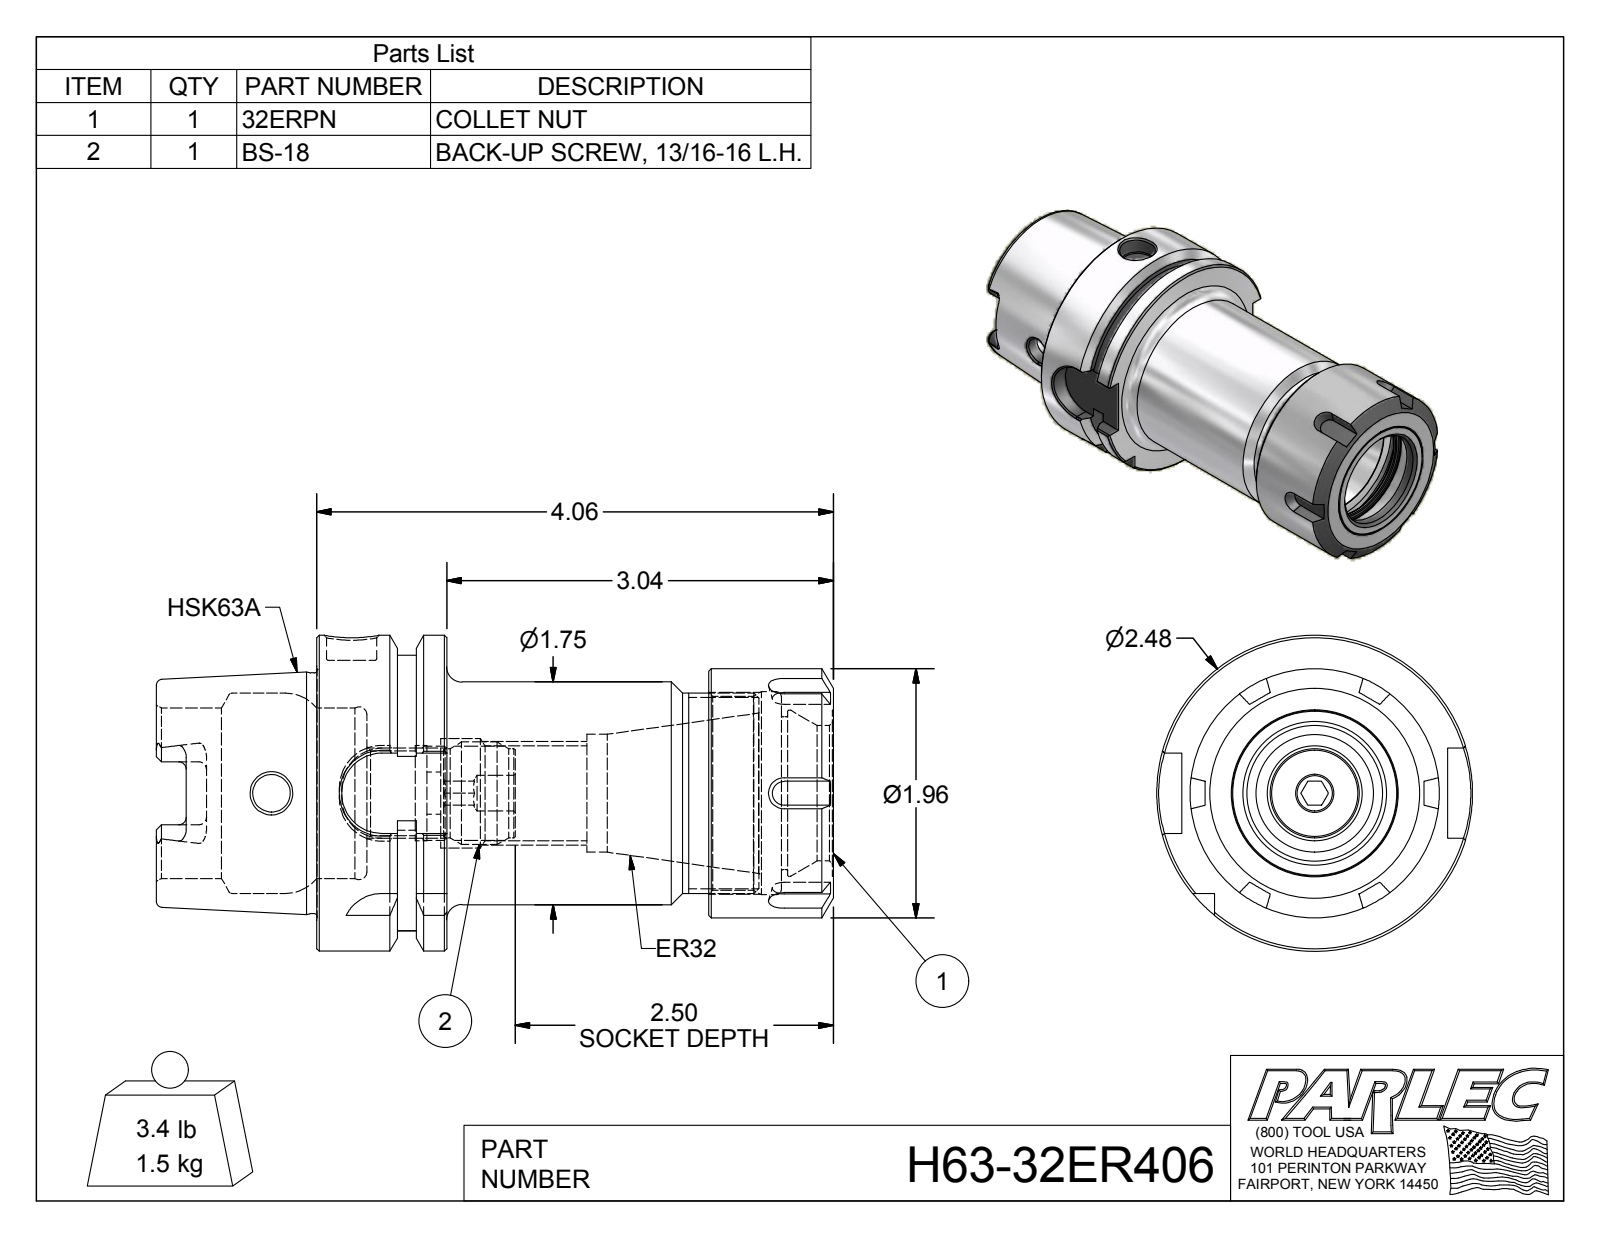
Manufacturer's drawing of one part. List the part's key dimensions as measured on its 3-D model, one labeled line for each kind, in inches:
Part name (STEP PRODUCT): H63-32ER406; H63-32ER4-1; 32ERPN; BS-18
STEP written by: Autodesk Inventor 2012 (AUTOMOTIVE_DESIGN)
Units: inches
Bodies: 3 solids, 207 faces (84 planar, 47 cylindrical, 76 other)
Overall size (bounding box): 5.32 × 2.48 × 2.48
Volume: 10.35 in³ · Surface area: 71.38 in²
Round holes (diameter × count): ⌀0.28 ×1, ⌀0.295 ×1, ⌀0.331 ×1, ⌀0.394 ×1, ⌀0.666 ×1, ⌀0.745 ×1, ⌀0.749 ×1, ⌀0.861 ×1, ⌀0.925 ×1, ⌀1.063 ×1, ⌀1.2 ×1, ⌀1.305 ×1
Round bosses / shafts (diameter × count): ⌀2.48 ×1, ⌀1.958 ×1, ⌀1.891 ×1, ⌀1.75 ×1, ⌀0.805 ×1, ⌀0.7 ×1
Partial cylindrical surfaces — rounded edges, fillets, slot ends (radius × count): R0.059 ×6, R0.113 ×4, R0.315 ×4, R1.083 ×1
Main face-to-face distances: 1.024, 4.06, 3.036, 0.241, 0.389, 3.082, 2.058, 0.978, 0.394, 0.63
